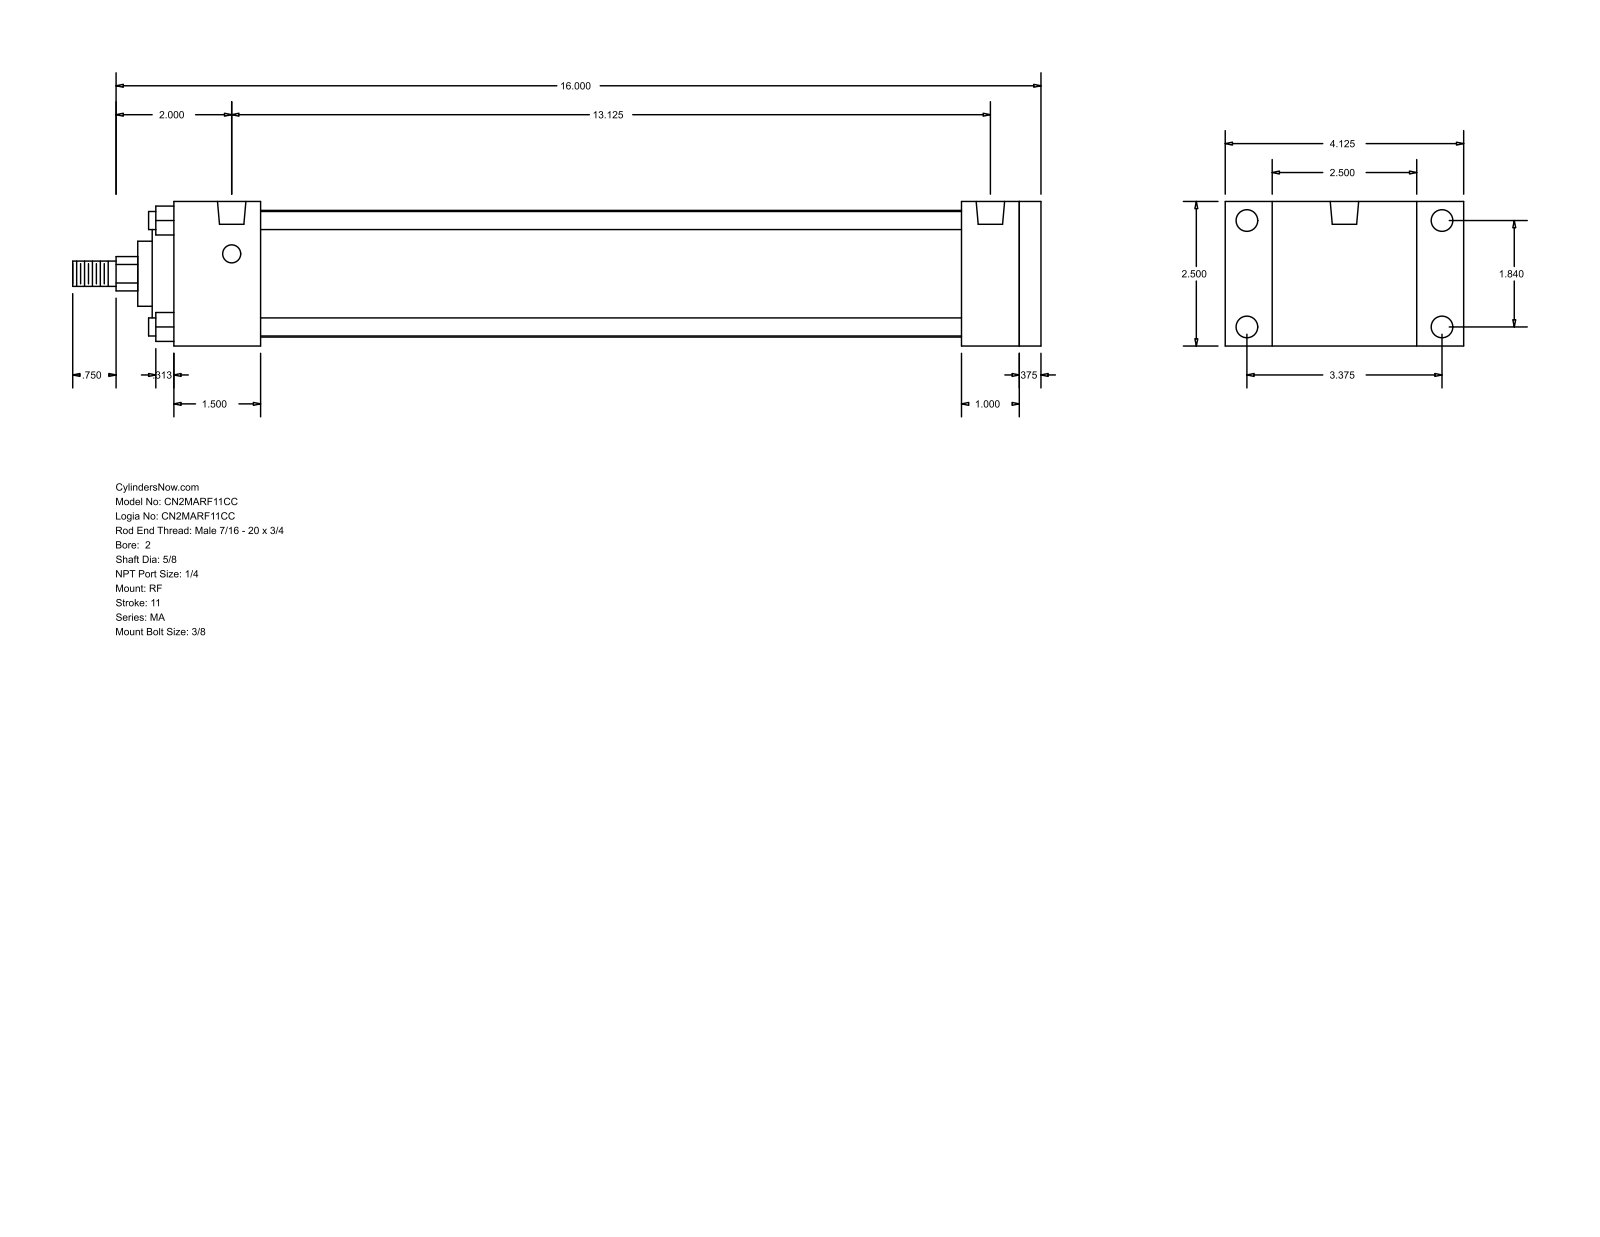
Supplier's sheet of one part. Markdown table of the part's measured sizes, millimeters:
| quantity | value |
| --- | --- |
| part name | MA_RF__0200_0.625 |
| STEP written by | GSSL Pune (CONFIG_CONTROL_DESIGN) |
| units | millimeters |
| bodies | 0 solids, 94 faces (65 planar, 29 cylindrical, 0 other) |
| overall size | 425.45 × 104.78 × 63.5 |
| round holes (diameter × count) | 7.94 × 4, 9.53 × 4, 12.49 × 2 |
| round bosses / shafts (diameter × count) | 7.94 × 4, 55.63 × 1, 50.8 × 1, 28.57 × 1, 15.88 × 1, 11.11 × 1 |
| partial cylindrical surfaces (radius × count) | 7.54 × 1 |
| main face-to-face distances | 63.5, 9.52, 381, 25.4, 38.1, 371.48, 333.38, 342.9, 346.08, 307.98 |
| hole center spacings | 46.74, 85.72, 97.63, 333.38 |
